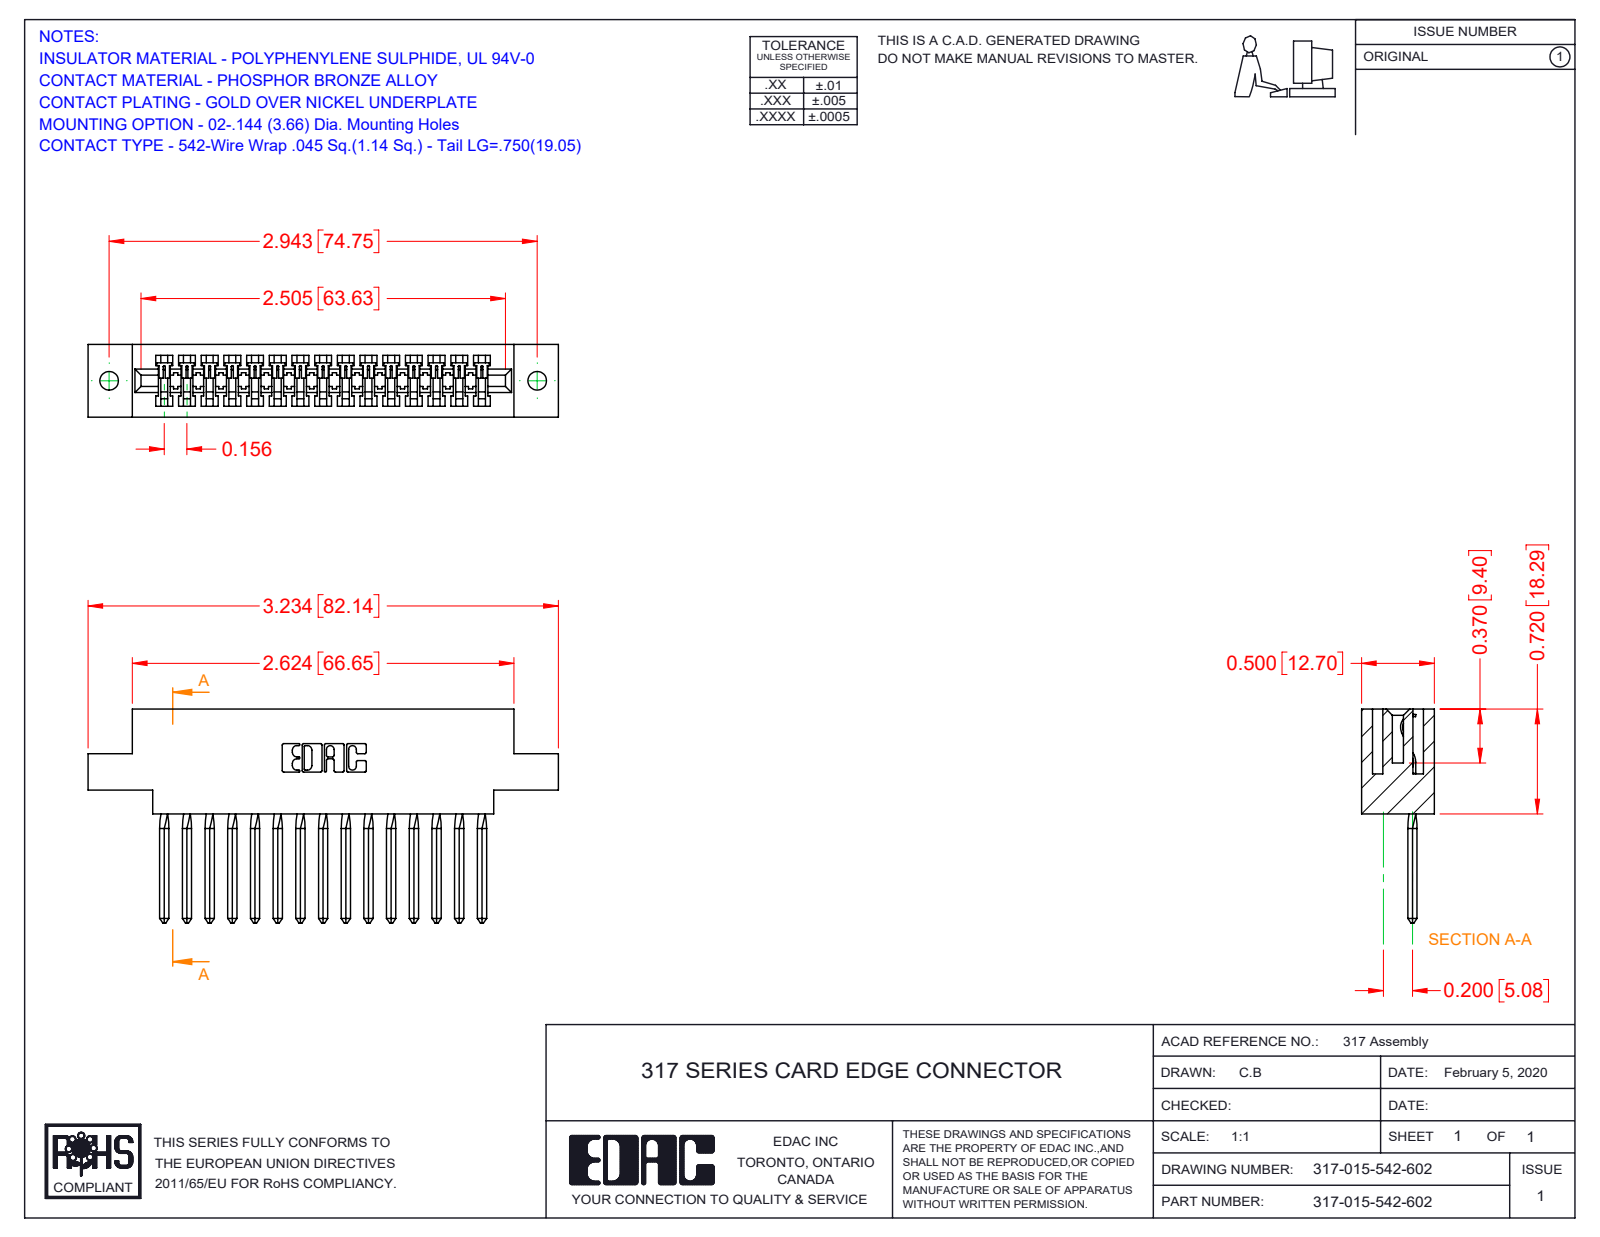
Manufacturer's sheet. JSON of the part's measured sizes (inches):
{"part_name": "317-015-542-602; 317-290-003_542; 317 Part_.144 Dia", "step_written_by": "SolidWorks 2016 (CONFIG_CONTROL_DESIGN)", "units": "inches", "bodies": {"solids": 16, "faces": 1227, "planar": 1018, "cylindrical": 149, "other": 60}, "overall_size": [3.234, 1.47, 0.5], "volume_in3": 0.728, "surface_area_in2": 21.21, "round_holes": [[0.128, 2]], "partial_cylinders_radius": [[0.006, 30], [0.01, 22], [0.007, 6], [0.031, 6], [0.026, 3], [0.074, 1], [0.089, 1], [0.1, 1]], "face_to_face_distances": [0.5, 0.075, 0.425, 0.11, 0.35, 0.065, 0.22, 0.136, 0.72, 0.279], "hole_center_spacings": [2.943]}
